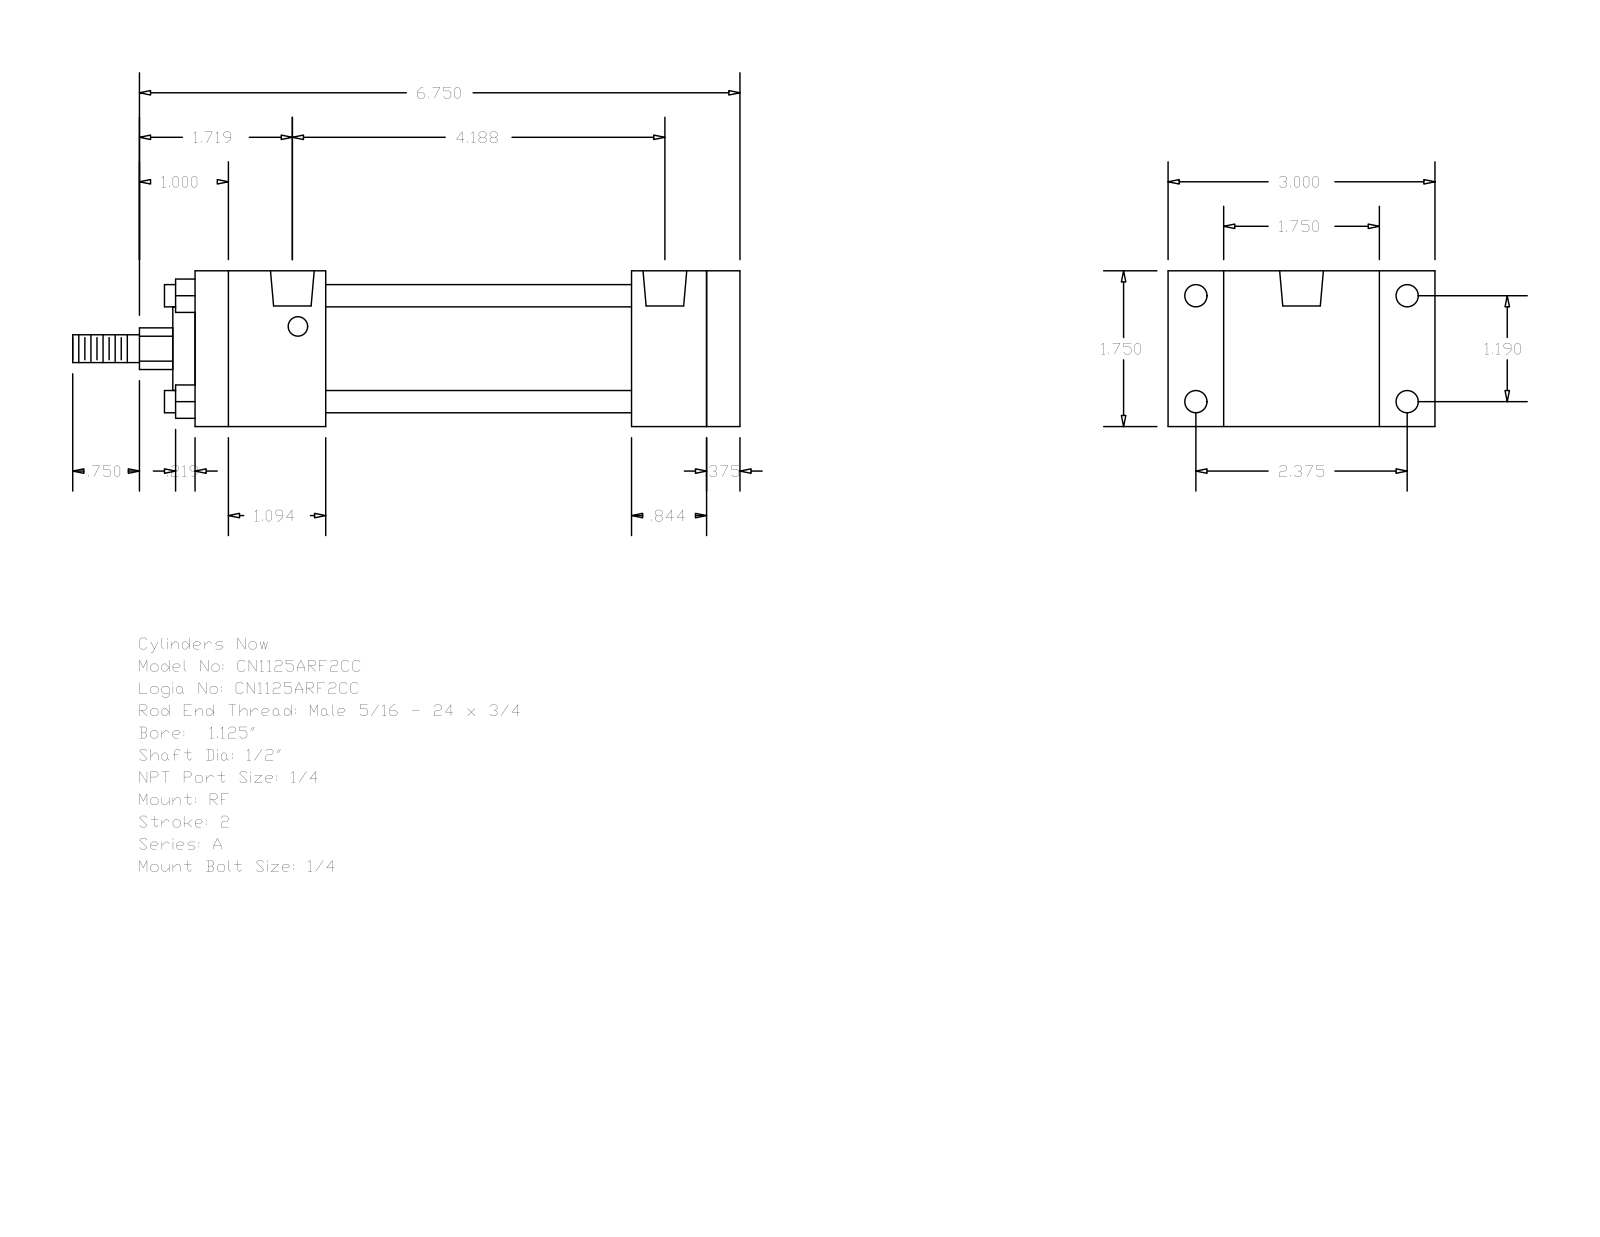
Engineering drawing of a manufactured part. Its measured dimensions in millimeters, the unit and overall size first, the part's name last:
Units: millimetres
Overall size (bounding box): 190.5 × 76.2 × 44.45
Round holes (diameter × count): ⌀5.56 ×4, ⌀6.35 ×4, ⌀12.49 ×2
Round bosses / shafts (diameter × count): ⌀6.35 ×4, ⌀31.88 ×1, ⌀23.81 ×1, ⌀12.7 ×1, ⌀7.94 ×1
Partial cylindrical surfaces — rounded edges, fillets, slot ends (radius × count): R5.94 ×1
Main face-to-face distances: 44.46, 9.52, 146.05, 155.57, 37.3, 124.61, 87.31, 108.75, 118.27, 21.44
Hole centre spacings: 30.22, 60.32, 67.47, 103.19, 1.58, 1.59, 104.77, 104.78
Bodies: 0 solids, 92 faces (64 planar, 28 cylindrical, 0 other)
Part name (STEP PRODUCT): A_RF__0112_0.5
STEP written by: GSSL Pune (CONFIG_CONTROL_DESIGN)
